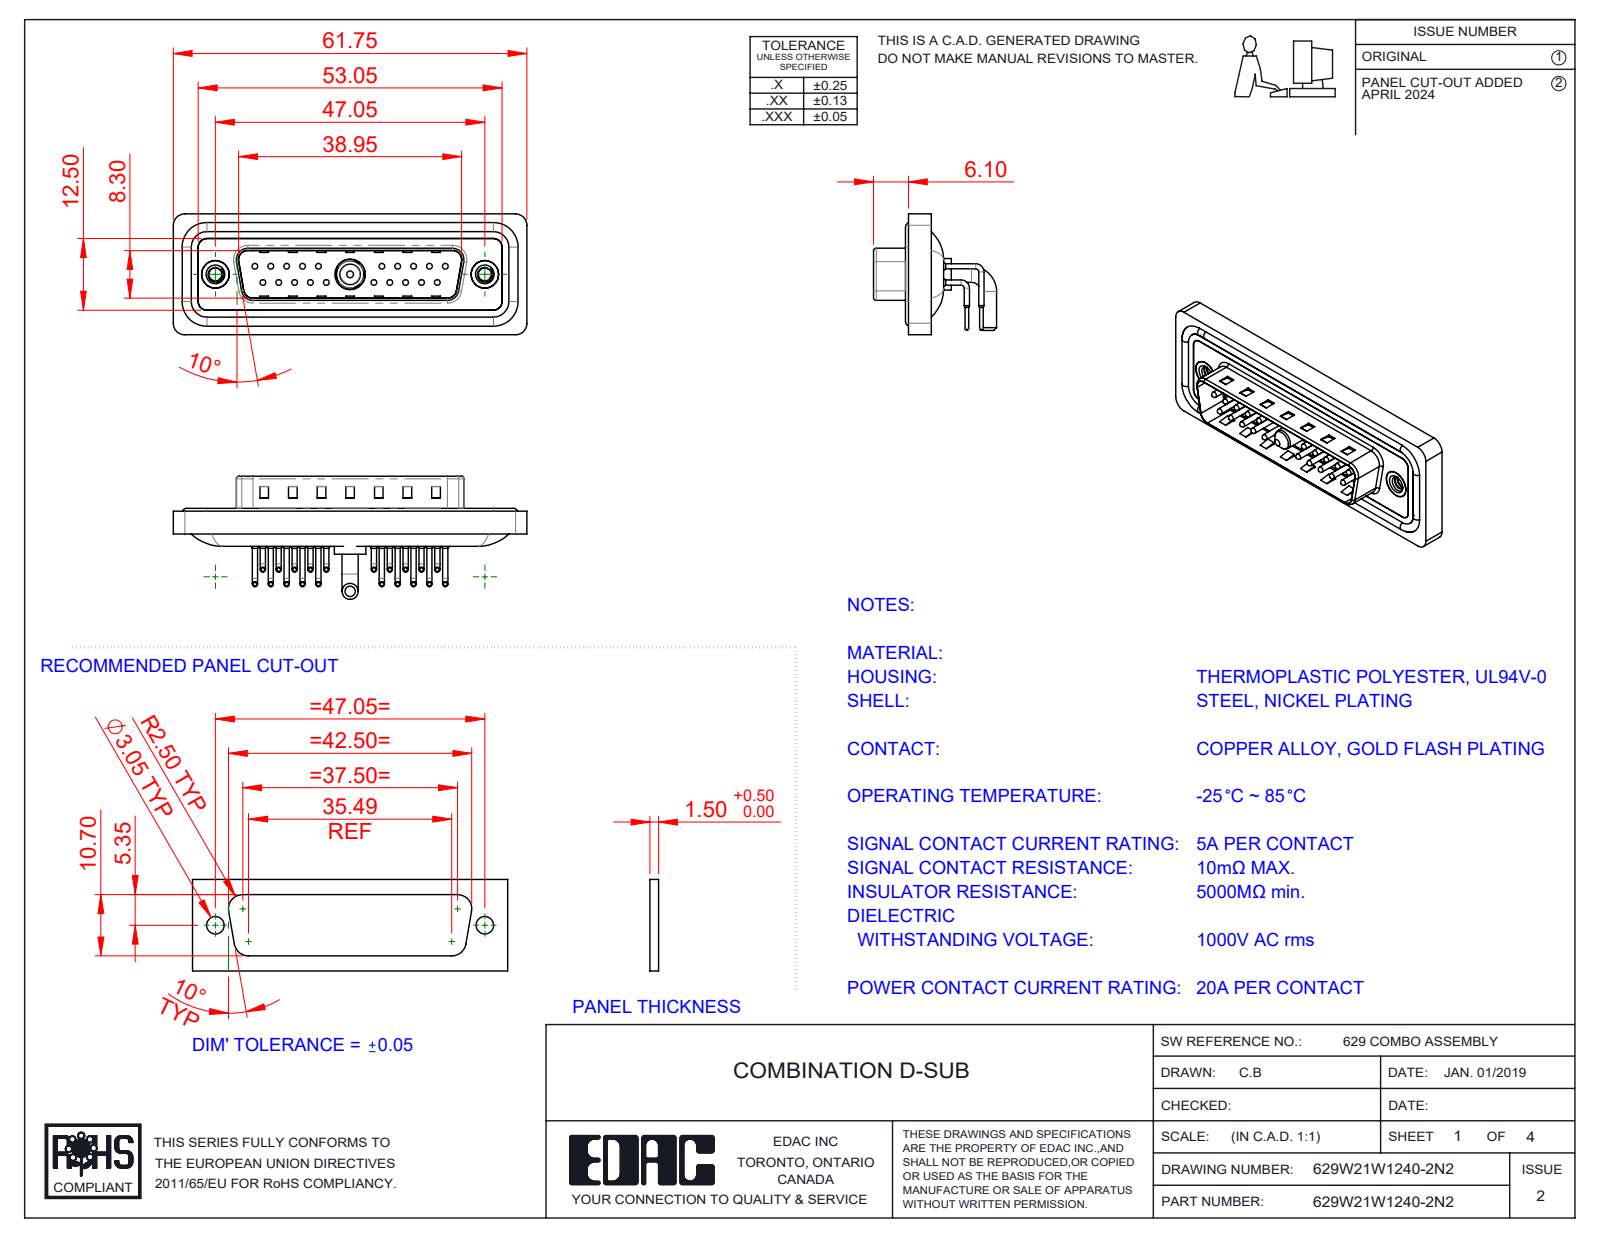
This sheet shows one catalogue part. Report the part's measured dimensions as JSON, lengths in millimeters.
{"part_name": "629Combo Contact Row 1; 629Combo Shell Rear_25 Contacts; 629Combo Threaded Rivet_2; 629Combo Shell Front_25 Contacts (+5 more)", "step_written_by": "SolidWorks 2023 (CONFIG_CONTROL_DESIGN)", "units": "millimeters", "bodies": {"solids": 29, "faces": 2726, "planar": 1499, "cylindrical": 929, "other": 298}, "overall_size": [61.75, 21.5, 21.1], "volume_mm3": 7429, "surface_area_mm2": 12721, "round_holes": [[0.75, 20], [1.6, 20], [2, 20], [2.26, 2], [4, 2], [4.8, 2], [5, 2], [4.85, 1], [5.3, 1]], "round_bosses_or_shafts": [[0.9, 40], [1.5, 20], [1, 20], [0.65, 20], [1.6, 4], [4.9, 2], [2.8, 2], [5.5, 1]], "partial_cylinders_radius": [[1.01, 20], [1.5, 18], [2, 18], [0.5, 8], [1.6, 8], [0.25, 4], [0.6, 4], [0.65, 4]], "face_to_face_distances": [0.4, 2.9, 0.8, 4.1, 1.1, 2.1, 1.6, 4.5, 1.5, 2.5], "hole_center_spacings": [3.16, 2.77, 5.54, 8.31, 5.04, 19.39, 20.97, 22.16]}
